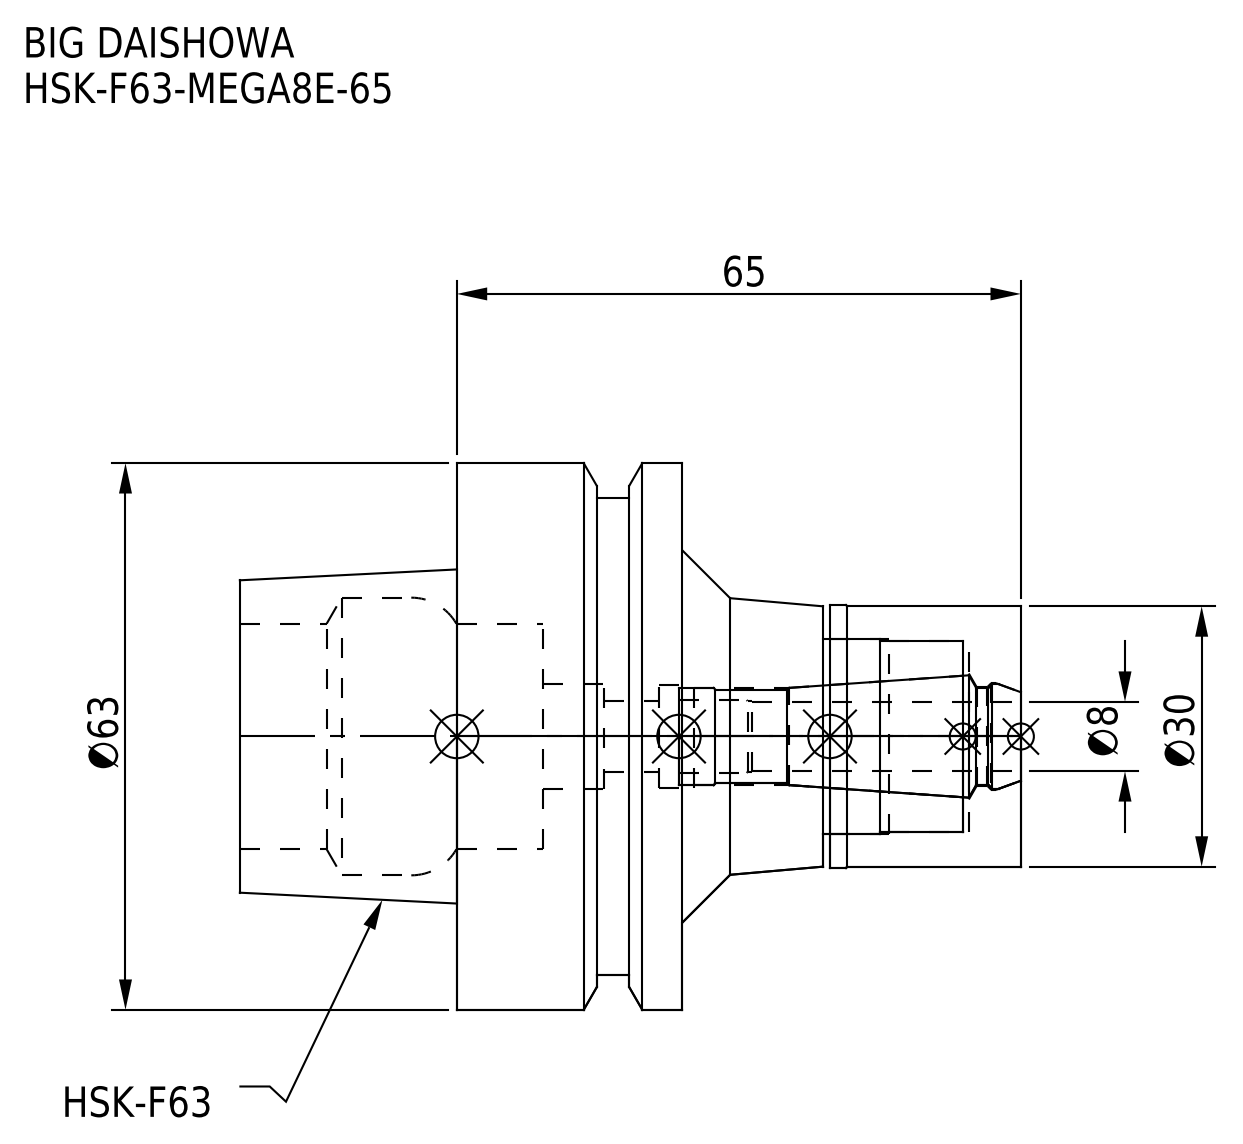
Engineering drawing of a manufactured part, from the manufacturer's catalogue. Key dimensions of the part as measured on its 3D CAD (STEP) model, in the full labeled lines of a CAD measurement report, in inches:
Part name (STEP PRODUCT): HF63ME08065-080_ASM.stp; DXF_TEMP_ASSY_ASM_4_ASM.stp; HSK-F63-MEGA8E-65-080-FreeParts; HSK-F63-MEGA8E-65_1.stp (+3 more)
STEP written by: SolidWorks 2019 (CONFIG_CONTROL_DESIGN)
Units: inches
Bodies: 2 solids, 78 faces (16 planar, 38 cylindrical, 24 other)
Overall size (bounding box): 3.543 × 2.48 × 2.48
Volume: 6.514 in³ · Surface area: 41.95 in²
Round holes (diameter × count): ⌀0.325 ×1, ⌀0.441 ×1, ⌀0.449 ×1, ⌀0.465 ×1, ⌀0.472 ×1, ⌀0.484 ×1, ⌀0.866 ×1, ⌀0.886 ×1, ⌀1.024 ×1, ⌀1.26 ×1
Round bosses / shafts (diameter × count): ⌀2.48 ×1, ⌀2.165 ×1, ⌀1.193 ×1, ⌀1.181 ×1
Main face-to-face distances: 1.024, 1.535, 2.559, 3.543, 2.008, 0.984, 2.167, 0.632, 0.392, 1.376
